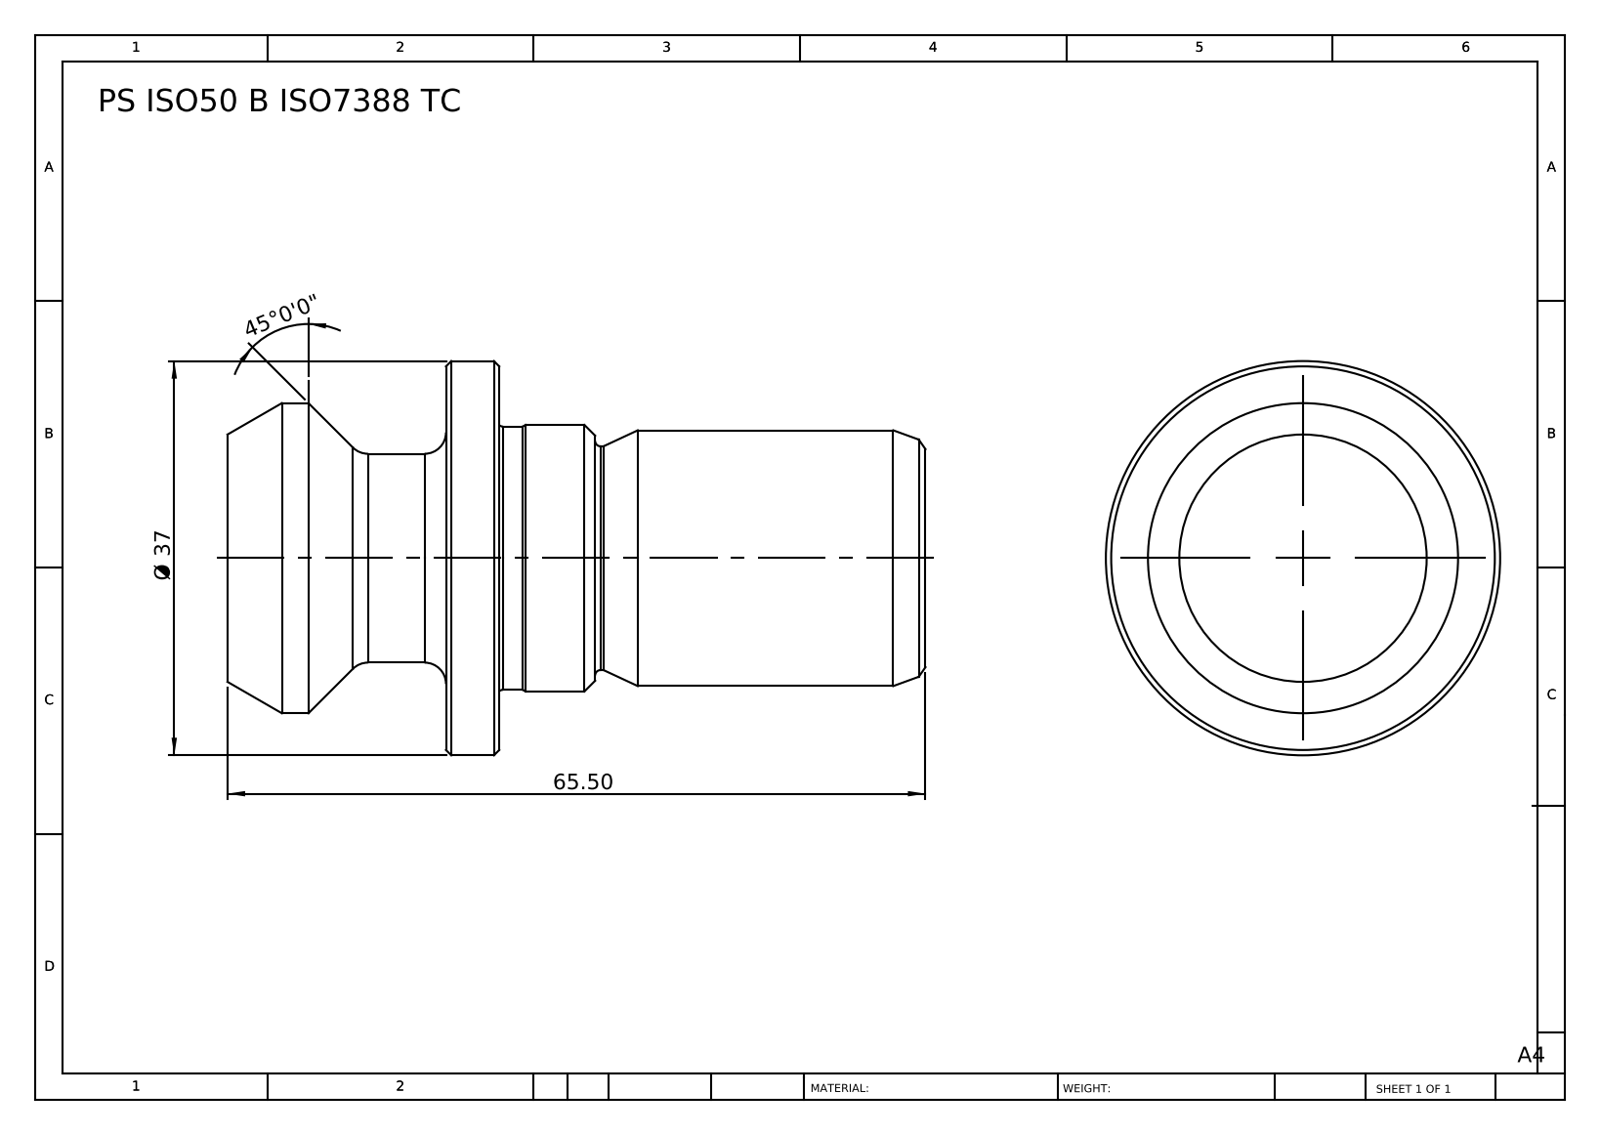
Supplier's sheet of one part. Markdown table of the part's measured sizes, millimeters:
| quantity | value |
| --- | --- |
| part name | PS ISO50 B ISO7388 TC |
| STEP written by | SolidWorks 2014 (CONFIG_CONTROL_DESIGN) |
| units | millimeters |
| bodies | 1 solid, 47 faces (5 planar, 14 cylindrical, 28 other) |
| overall size | 65.5 × 37 × 37 |
| volume | 32 502 mm³ |
| surface area | 7 462 mm² |
| round bosses / shafts (diameter × count) | 37 × 1, 29.1 × 1, 25 × 1, 24.7 × 1, 24 × 1, 21 × 1, 19.6 × 1 |
| main face-to-face distances | 5, 25.5, 20.5, 40, 45, 65.5, 31, 9, 14, 34.5 |
